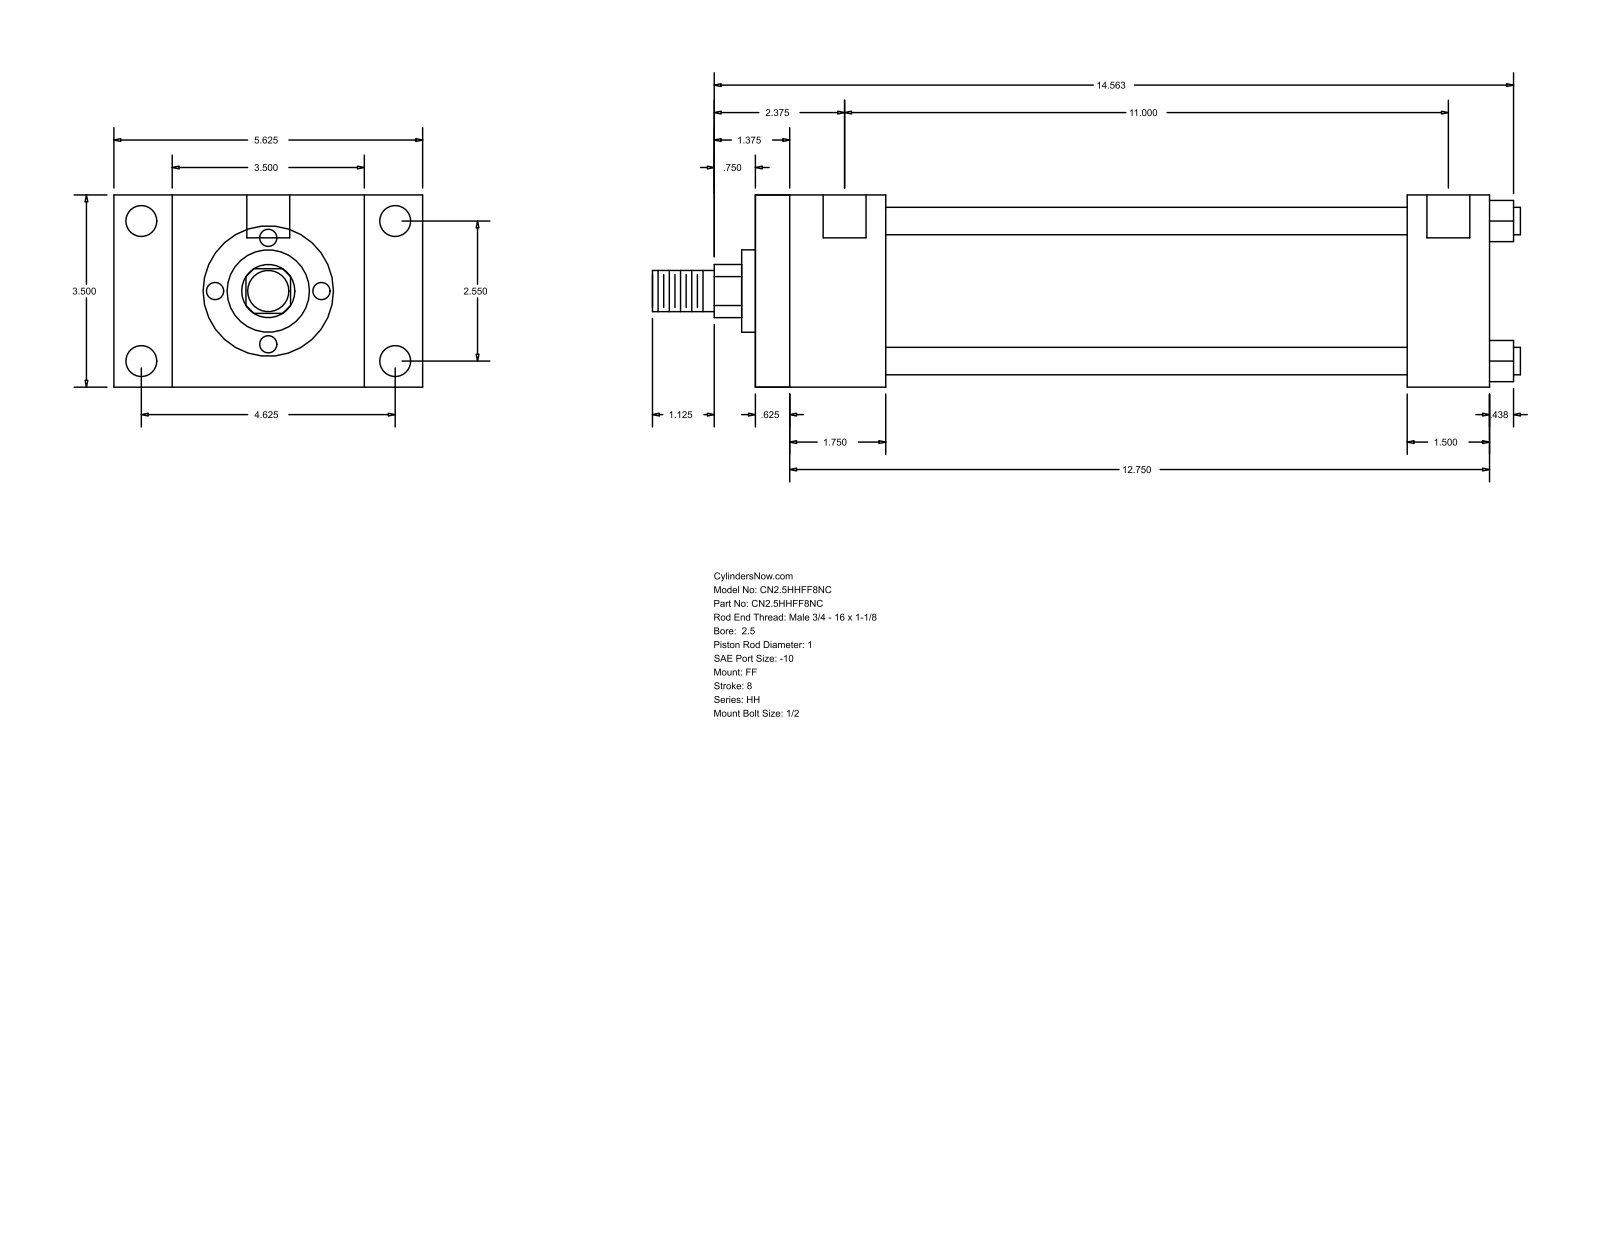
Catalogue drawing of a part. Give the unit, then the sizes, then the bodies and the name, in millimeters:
Units: millimetres
Overall size (bounding box): 401.64 × 142.88 × 88.9
Round holes (diameter × count): ⌀5.56 ×4, ⌀14.3 ×4, ⌀19.84 ×2
Round bosses / shafts (diameter × count): ⌀12.7 ×4, ⌀73.03 ×1, ⌀38.1 ×1, ⌀25.4 ×1, ⌀19.05 ×1
Partial cylindrical surfaces — rounded edges, fillets, slot ends (radius × count): R12.29 ×1
Main face-to-face distances: 88.9, 339.72, 15.87, 323.85, 60.33, 44.46, 279.39, 301.63, 285.76, 241.3
Hole centre spacings: 64.76, 117.48, 134.15, 282.57, 1.58, 1.59, 279.4, 280.98
Bodies: 0 solids, 92 faces (64 planar, 28 cylindrical, 0 other)
Part name (STEP PRODUCT): HH_FF__0250_1
STEP written by: GSSL Pune (CONFIG_CONTROL_DESIGN)
